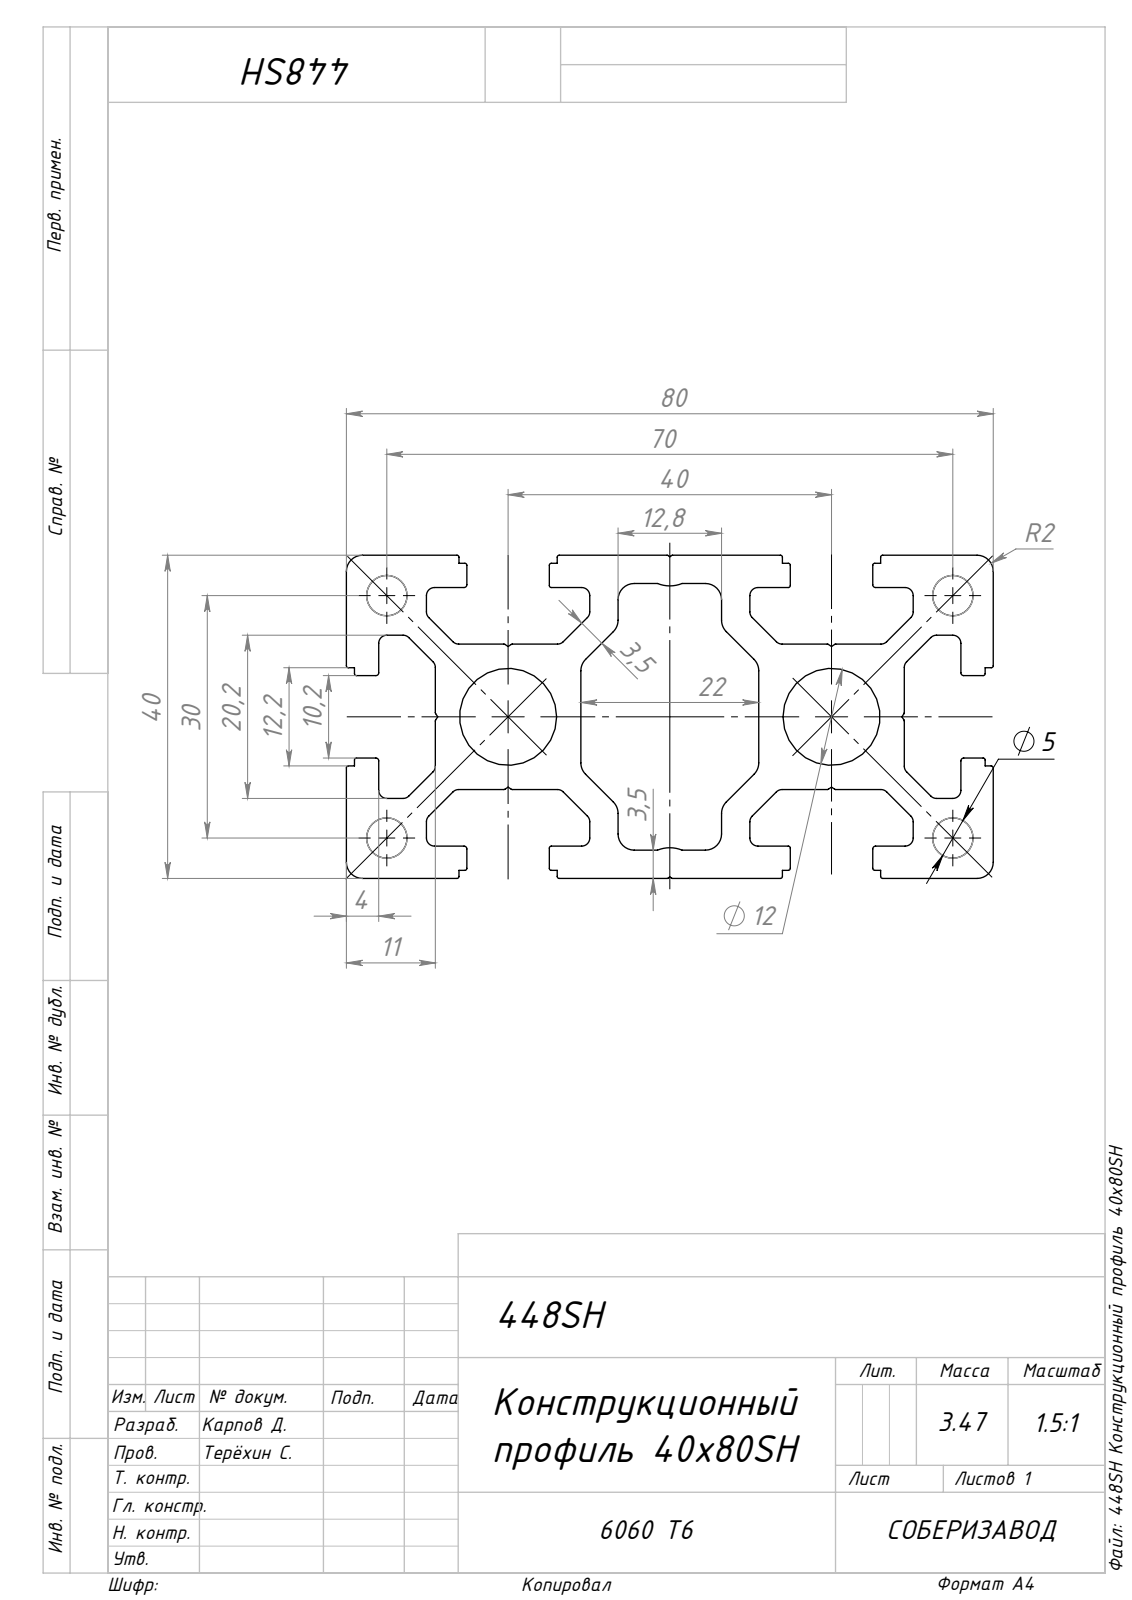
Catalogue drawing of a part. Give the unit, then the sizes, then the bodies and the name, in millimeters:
Units: millimetres
Overall size (bounding box): 1000 × 80 × 40
Round holes (diameter × count): ⌀5 ×4, ⌀12 ×2
Partial cylindrical surfaces — rounded edges, fillets, slot ends (radius × count): R0.25 ×44, R1 ×36, R2 ×16, R0.35 ×8, R4 ×2
Main face-to-face distances: 40, 29, 11, 3.5, 18, 4, 7, 25, 28.28, 36
Hole centre spacings: 21.21, 57.01, 30, 70, 76.16, 40
Volume: 1 285 000 mm³ · Surface area: 690 395 mm²
Bodies: 1 solid, 254 faces (128 planar, 126 cylindrical, 0 other)
Part name (STEP PRODUCT): 448SH Конструкционный профиль 40х80SH; 448SH Конструкционный профиль 40х80SH_00
STEP written by: SolidWorks 2025 (CONFIG_CONTROL_DESIGN)
